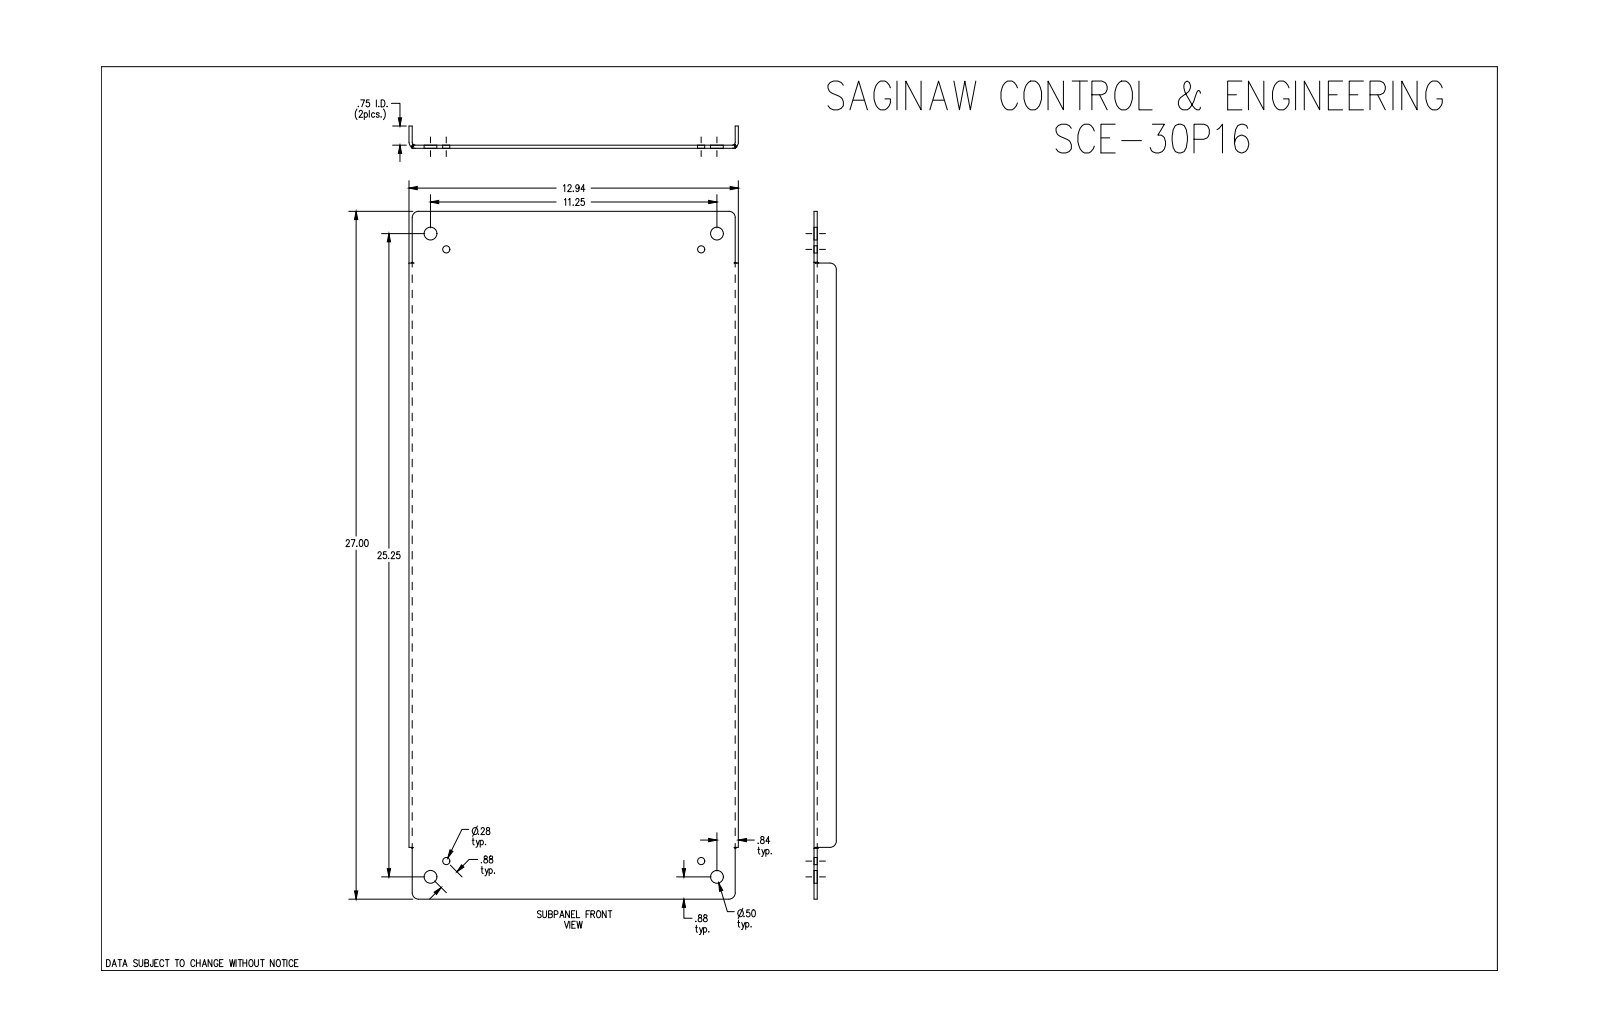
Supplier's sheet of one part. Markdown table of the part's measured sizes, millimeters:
| quantity | value |
| --- | --- |
| part name | SCE-30P16 |
| STEP written by | SolidWorks 2019 (CONFIG_CONTROL_DESIGN) |
| units | millimeters |
| bodies | 1 solid, 50 faces (18 planar, 20 cylindrical, 12 other) |
| overall size | 685.8 × 328.6 × 22.2 |
| volume | 774 600 mm³ |
| surface area | 495 300 mm² |
| round holes (diameter × count) | 7.1 × 4, 12.7 × 4 |
| partial cylindrical surfaces (radius × count) | 6.4 × 6, 2.8 × 2, 6 × 2 |
| main face-to-face distances | 3.2, 3.2, 325.5, 322.2, 328.6, 19.1, 22.2, 685.8, 51.6, 634.2 |
| hole center spacings | 22.2, 270.5, 625.8, 681.4, 254.3, 285.8, 609.9, 641.4 |
